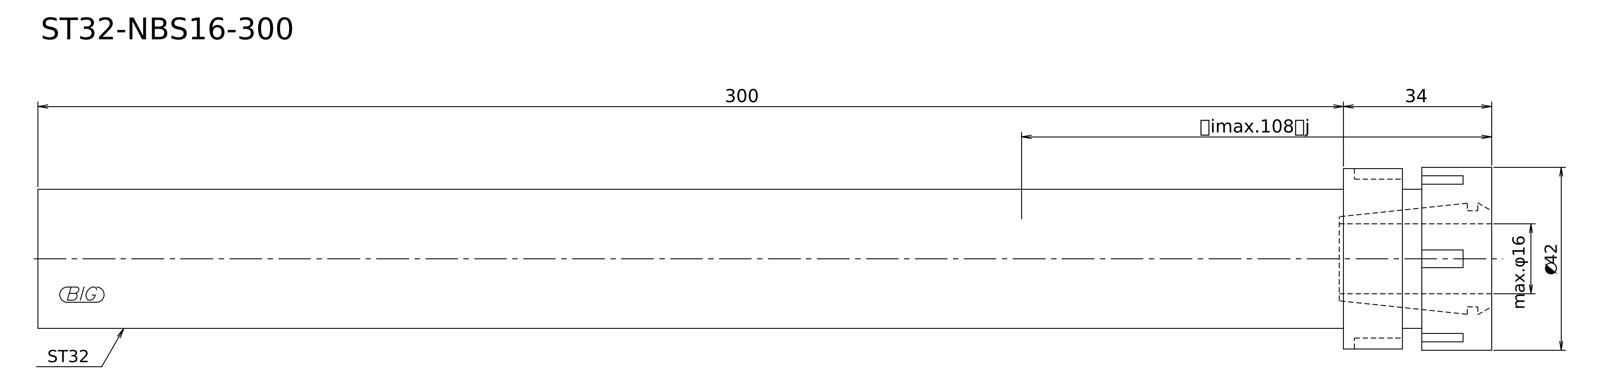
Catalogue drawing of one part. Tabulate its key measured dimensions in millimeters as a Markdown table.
| quantity | value |
| --- | --- |
| STEP written by | Kubotek KeyCreator V8.5.1 (14335) (CONFIG_CONTROL_DESIGN) |
| units | millimeters |
| bodies | 1 solid, 9 faces (5 planar, 4 cylindrical, 0 other) |
| overall size | 334 × 42 × 42 |
| volume | 285 321 mm³ |
| surface area | 38 351 mm² |
| round bosses / shafts (diameter × count) | 42 × 1, 41.5 × 1, 32 × 1 |
| main face-to-face distances | 334, 16, 318, 20.5, 4.5, 313.5, 34, 18, 13.5, 300 |
